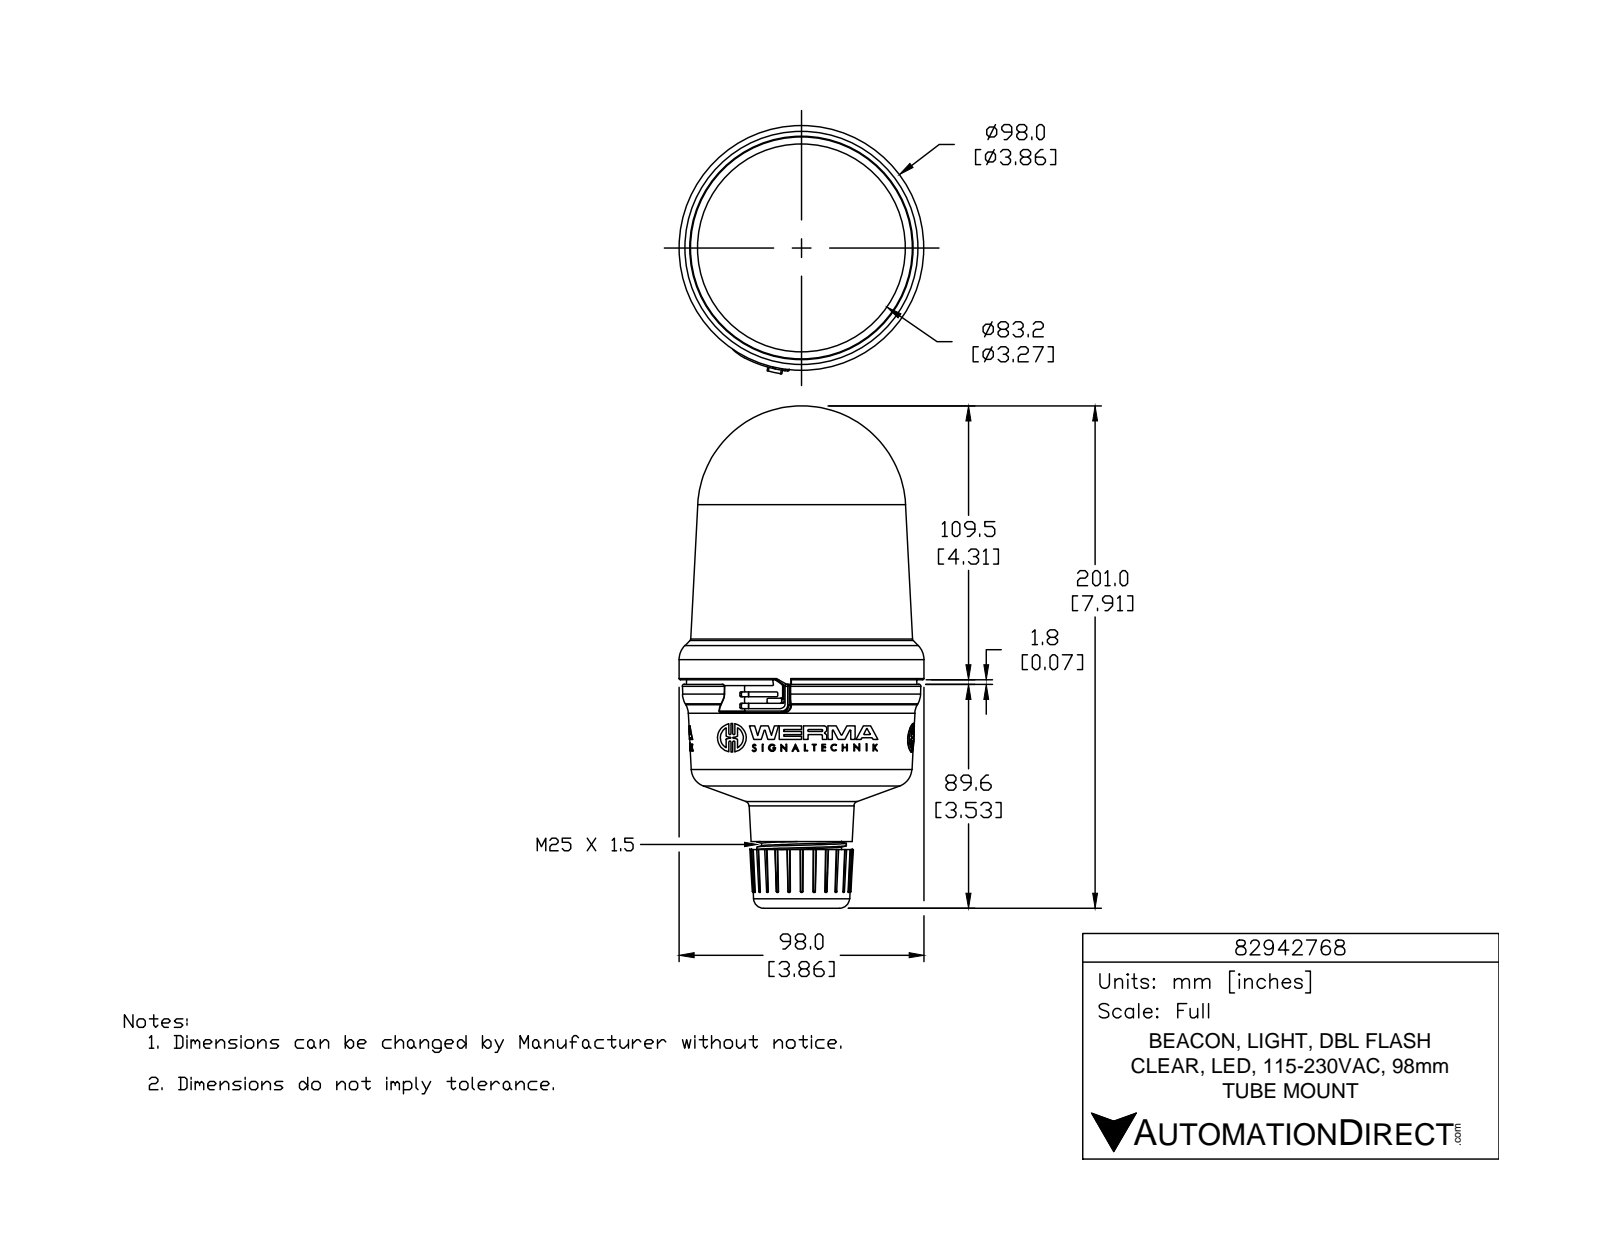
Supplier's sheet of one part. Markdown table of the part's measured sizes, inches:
| quantity | value |
| --- | --- |
| part name | 82942768 |
| STEP written by | SolidWorks 2015 (AUTOMOTIVE_DESIGN) |
| units | inches |
| bodies | 1 solid, 1006 faces (554 planar, 189 cylindrical, 263 other) |
| overall size | 7.914 × 3.912 × 3.858 |
| volume | 54.7 in³ |
| surface area | 91.39 in² |
| round holes (diameter × count) | 0.078 × 3, 1.013 × 1, 1.024 × 1 |
| round bosses / shafts (diameter × count) | 0.452 × 3, 0.113 × 3, 3.858 × 1, 1.409 × 1, 1.261 × 1 |
| partial cylindrical surfaces (radius × count) | 0.02 × 12, 0.007 × 9, 0.007 × 6, 0.016 × 6, 0.016 × 6, 0.016 × 6, 0.262 × 6, 0.006 × 3 |
| main face-to-face distances | 2.214, 0.462, 2.676, 0.335, 0.127, 2.548, 2.603, 2.476, 2.141, 0.073 |
